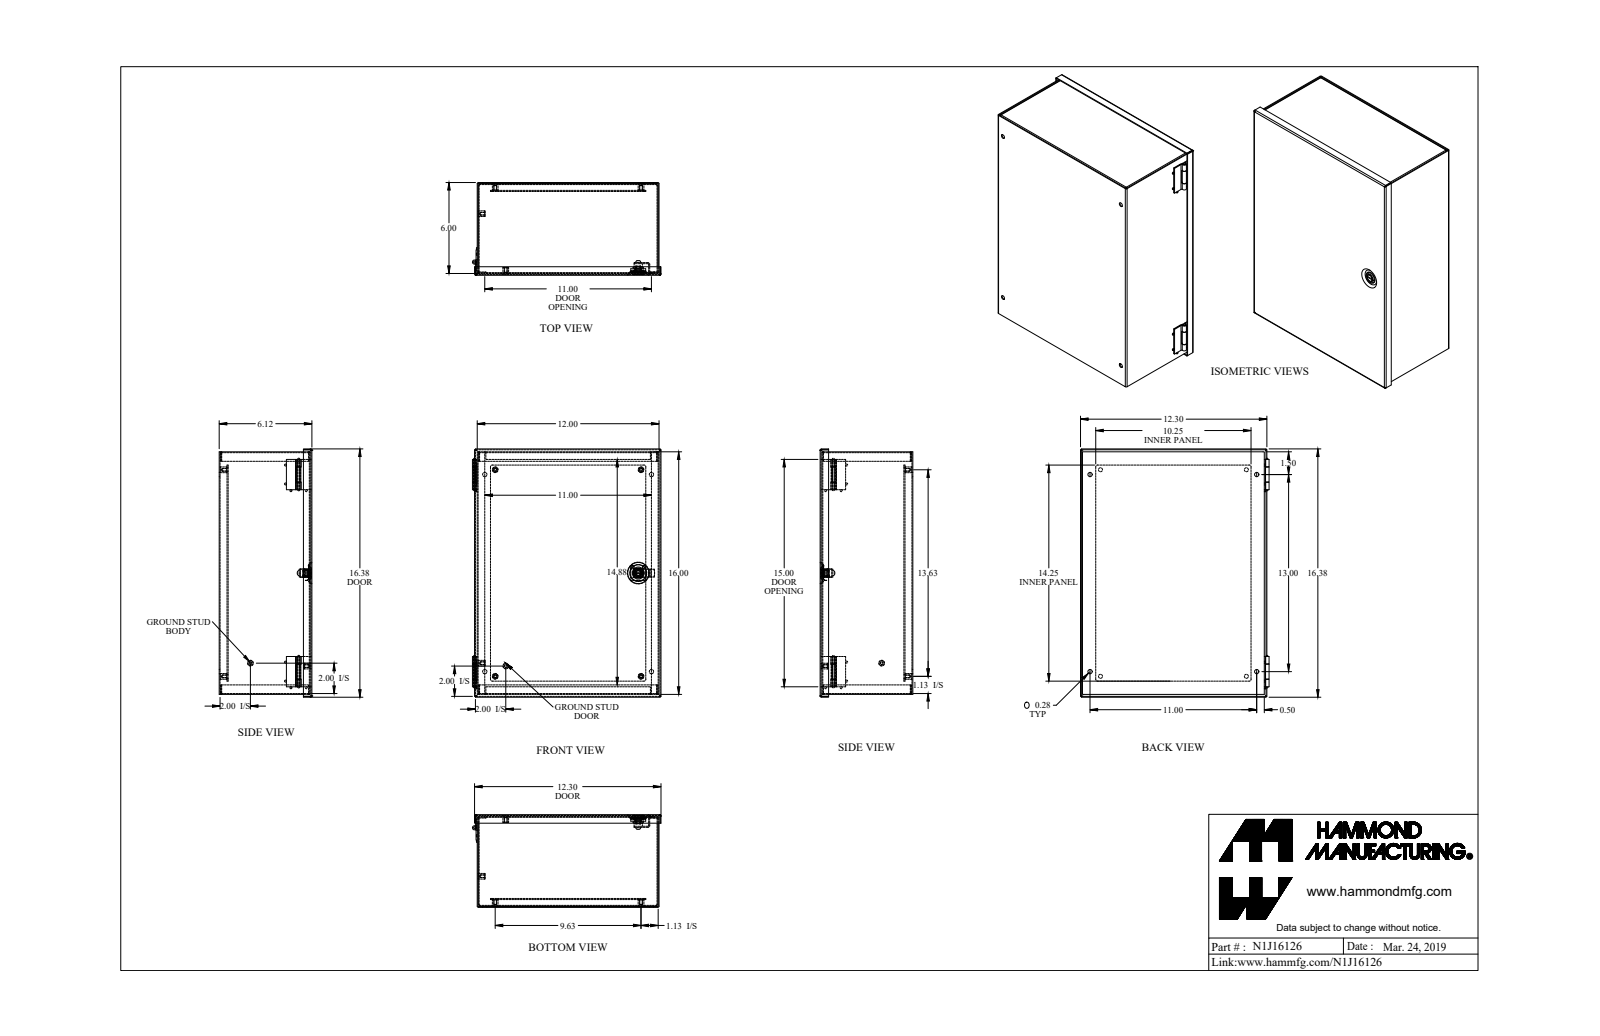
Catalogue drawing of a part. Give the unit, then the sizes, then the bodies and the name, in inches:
Units: inches
Overall size (bounding box): 16.38 × 12.443 × 6.118
Round holes (diameter × count): ⌀0.156 ×6, ⌀0.28 ×4, ⌀0.265 ×2, ⌀0.265 ×2, ⌀0.125 ×1, ⌀0.319 ×1, ⌀0.476 ×1
Round bosses / shafts (diameter × count): ⌀0.131 ×8, ⌀0.375 ×6, ⌀0.787 ×1, ⌀0.547 ×1, ⌀0.472 ×1, ⌀0.469 ×1, ⌀0.366 ×1, ⌀0.32 ×1
Partial cylindrical surfaces — rounded edges, fillets, slot ends (radius × count): R0.029 ×16, R0.086 ×16, R0.012 ×4, R0.1 ×4, R0.125 ×4, R0.036 ×2, R0.079 ×2, R0.25 ×2
Main face-to-face distances: 0.057, 6.061, 6.004, 6.118, 11.943, 0.072, 0.517, 0.46, 5.544, 5.601
Hole centre spacings: 0.755, 10.317, 13.33, 16.84, 6.558, 6.815, 9.625, 11
Volume: 57.18 in³ · Surface area: 1 936 in²
Bodies: 18 solids, 477 faces (224 planar, 188 cylindrical, 65 other)
Part name (STEP PRODUCT): N1J16126
STEP written by: SolidWorks 2018 (AUTOMOTIVE_DESIGN)
